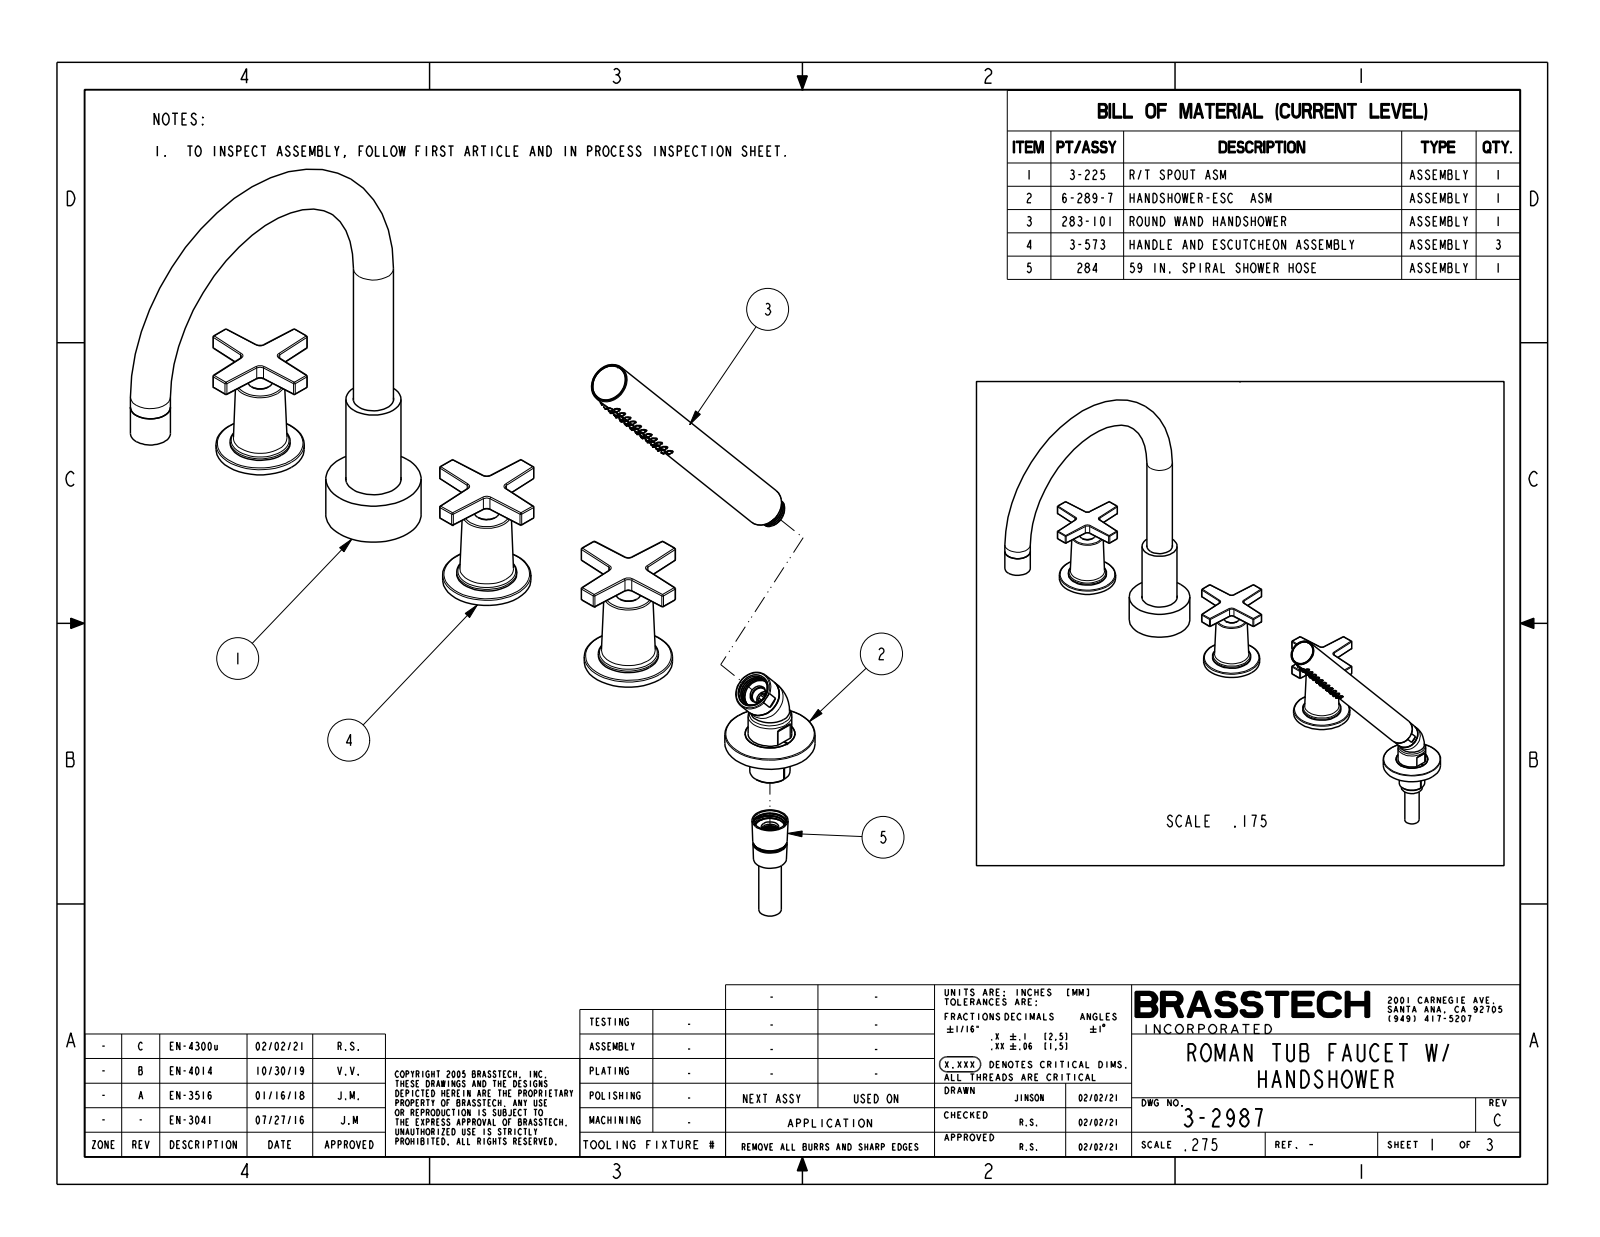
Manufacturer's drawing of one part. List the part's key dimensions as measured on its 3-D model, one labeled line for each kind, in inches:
Part name (STEP PRODUCT): 3-2987
STEP written by: CREO PARAMETRIC BY PTC INC, 2018400 (CONFIG_CONTROL_DESIGN)
Units: inches
Bodies: 6 solids, 1100 faces (76 planar, 360 cylindrical, 664 other)
Overall size (bounding box): 20.568 × 11.978 × 9.818
Volume: 44.58 in³ · Surface area: 209.8 in²
Round holes (diameter × count): ⌀0.14 ×44
Round bosses / shafts (diameter × count): ⌀2.2 ×3, ⌀1.5 ×3, ⌀1.275 ×3, ⌀1 ×3, ⌀0.625 ×3, ⌀0.525 ×3, ⌀2.375 ×1, ⌀2.25 ×1
Partial cylindrical surfaces — rounded edges, fillets, slot ends (radius × count): R0.03 ×88, R0.125 ×12, R0.05 ×6, R0.45 ×1, R0.56 ×1
Main face-to-face distances: 2.87, 0.187, 2.683, 2.495, 2.308, 0.375, 1.103, 0.916, 1.392, 1.767
Hole centre spacings: 0.17, 0.447, 0.604, 0.336, 0.672, 0.336, 0.887, 1.46
